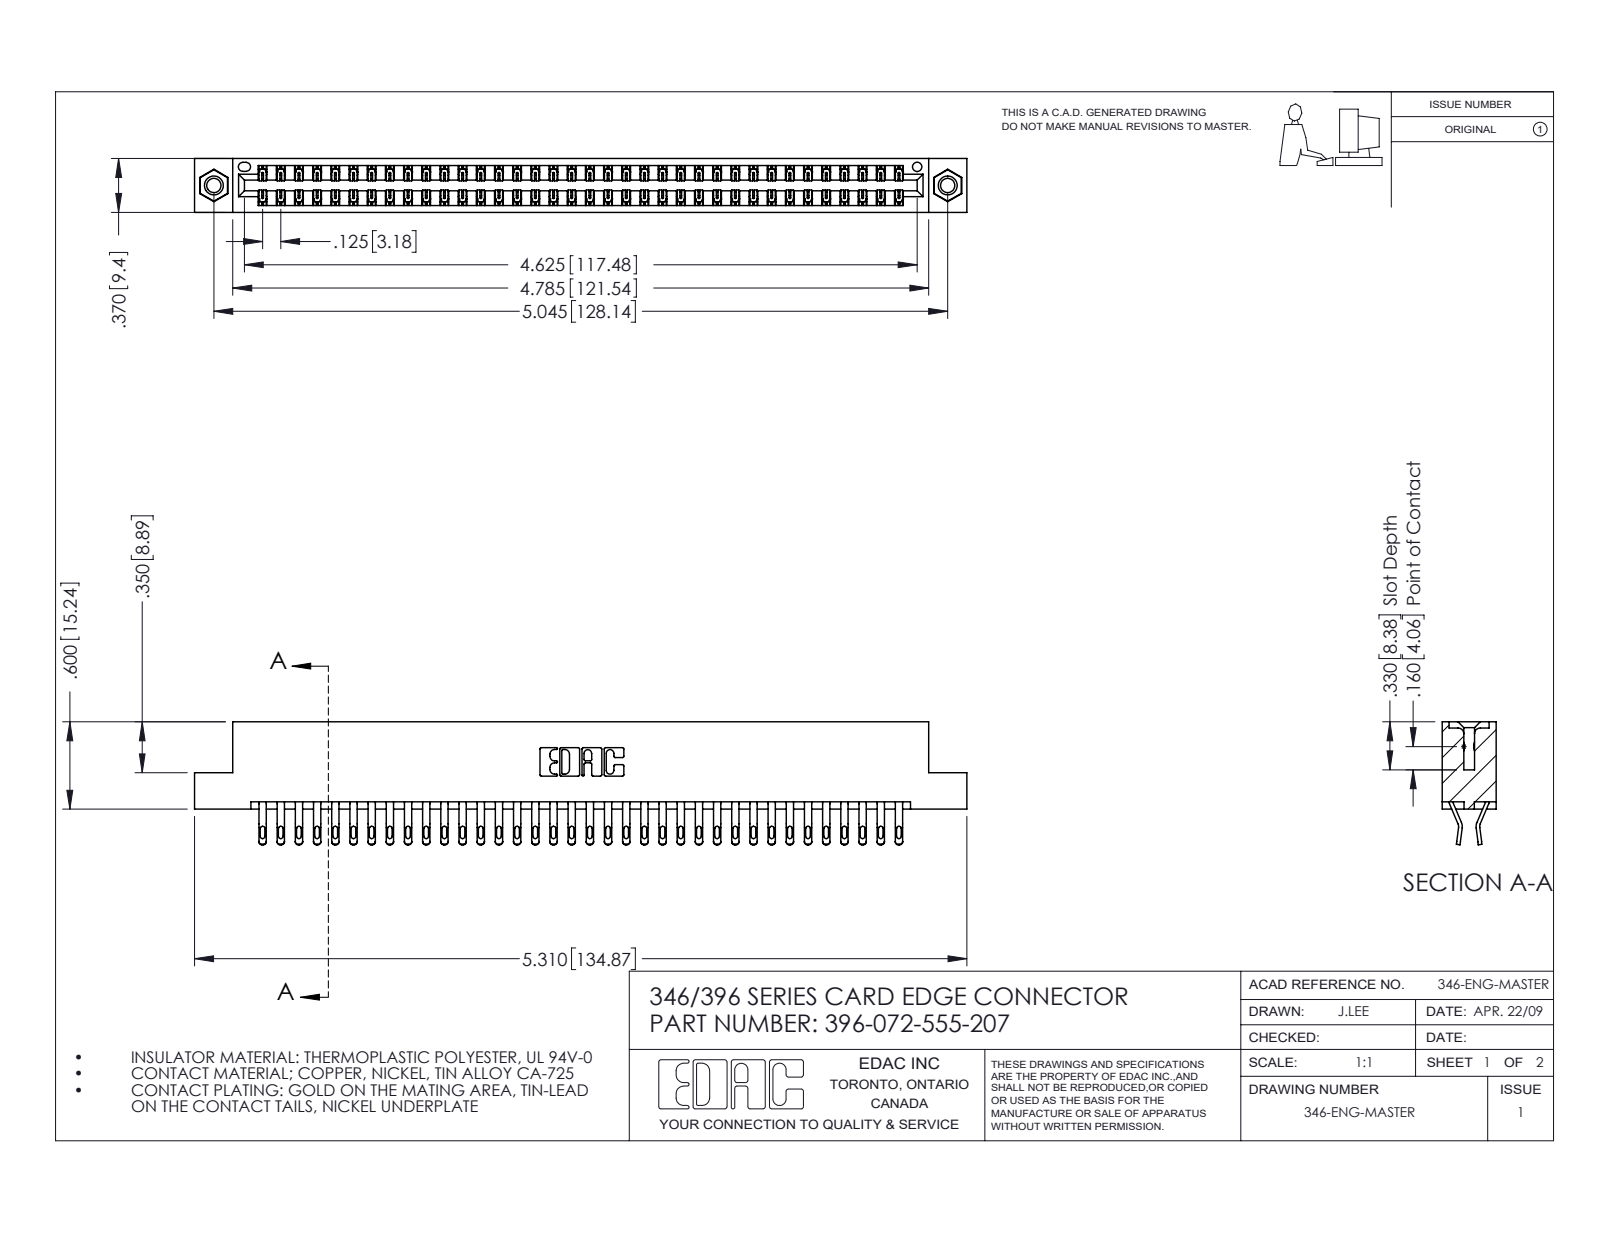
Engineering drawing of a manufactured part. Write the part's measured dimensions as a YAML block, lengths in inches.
part_name: "346 Part_Flush Mounting Lugs - 0.156 Dia-TI; 345-292-001_555 Tail; 396-072-555-207; 345-250-001_345-250-005-103"
step_written_by: "SolidWorks 2016 (CONFIG_CONTROL_DESIGN)"
units: inches
bodies: {solids: 75, faces: 4358, planar: 2484, cylindrical: 1858, other: 16}
overall_size: [5.31, 0.845, 0.37]
volume: 0.812
surface_area: 29.4
round_holes:
  - {diameter: 0.098, count: 2}
  - {diameter: 0.125, count: 2}
  - {diameter: 0.156, count: 2}
  - {diameter: 0.064, count: 1}
round_bosses_or_shafts:
  - {diameter: 0.155, count: 2}
partial_cylinders:
  - {radius: 0.016, count: 144}
  - {radius: 0.02, count: 144}
  - {radius: 0.006, count: 108}
  - {radius: 0.01, count: 22}
  - {radius: 0.007, count: 6}
  - {radius: 0.031, count: 6}
  - {radius: 0.026, count: 3}
  - {radius: 0.01, count: 2}
face_to_face_distances: [0.048, 0.322, 0.37, 0.25, 0.025, 0.072, 0.298, 0.275, 0.148, 0.222]
hole_center_spacings: [0.246, 4.836, 5.045]
